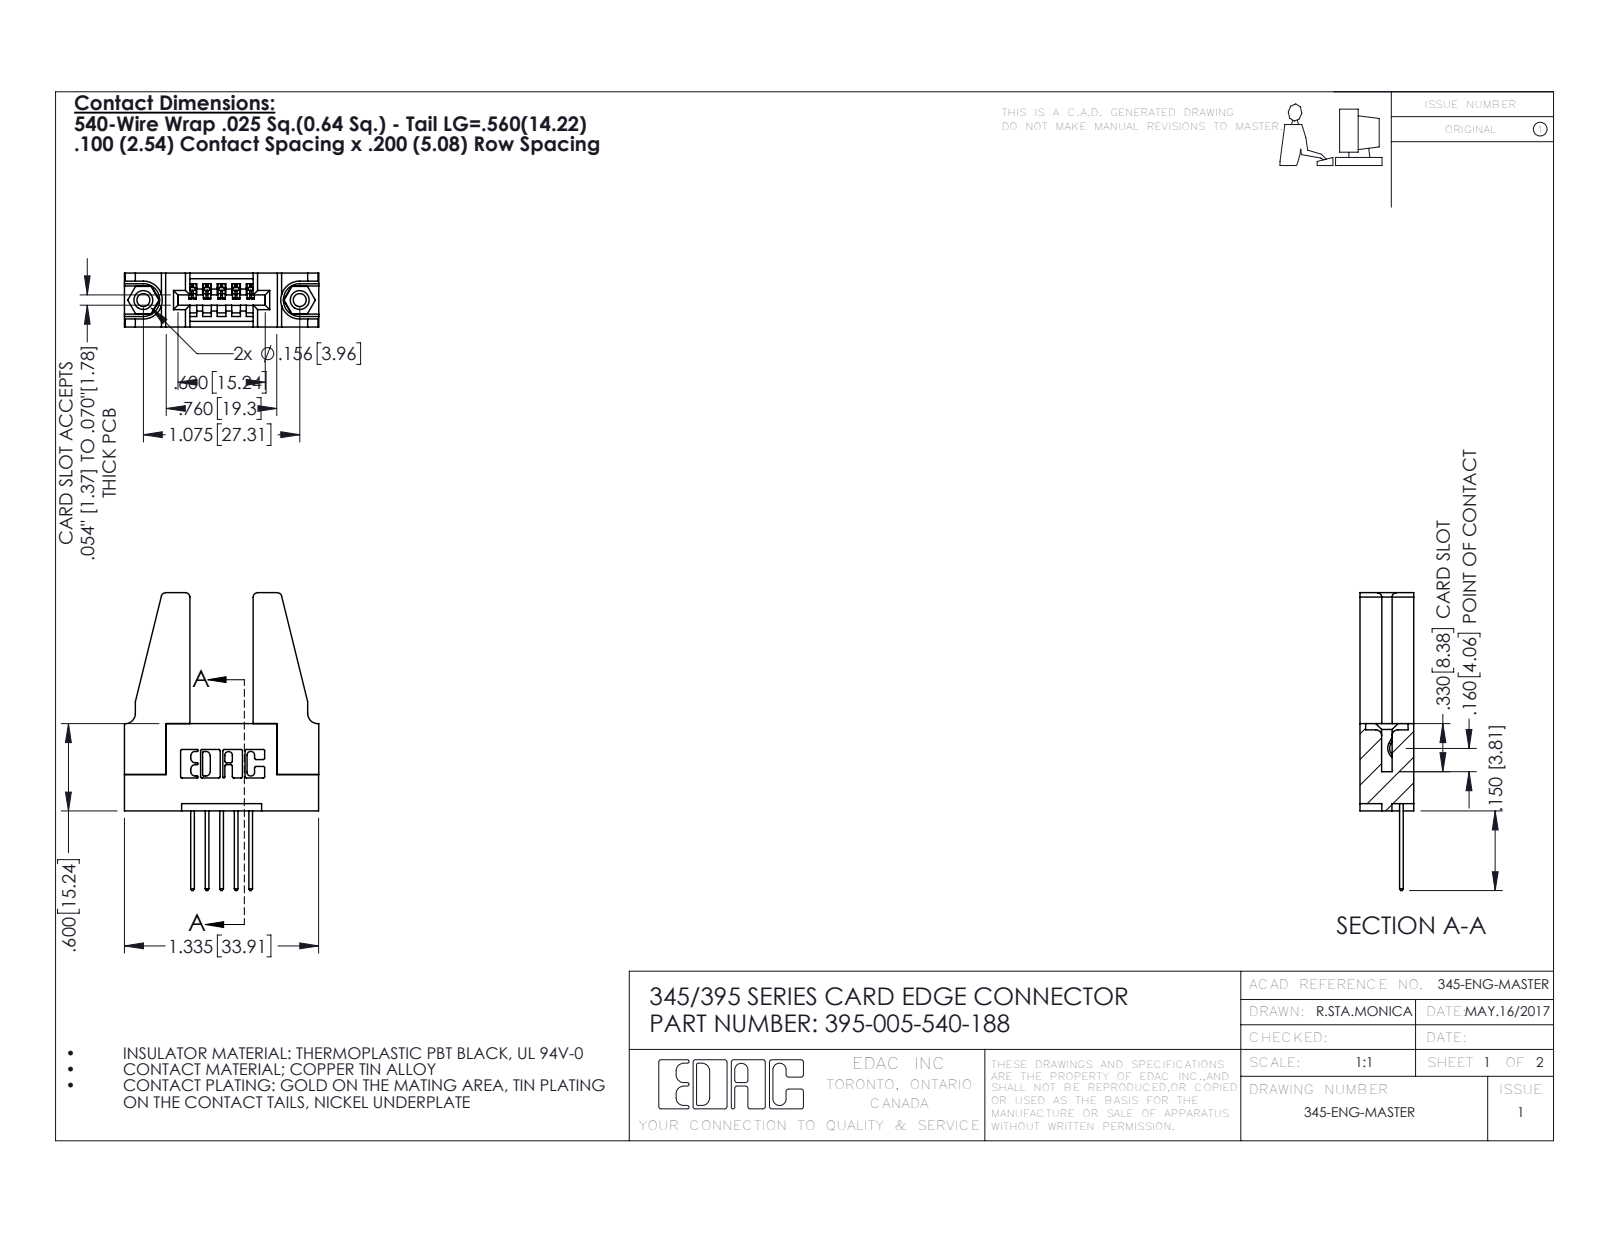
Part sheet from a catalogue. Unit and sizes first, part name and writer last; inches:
Units: inches
Overall size (bounding box): 2.047 × 1.336 × 0.37
Round holes (diameter × count): ⌀0.089 ×2, ⌀0.125 ×2, ⌀0.156 ×2, ⌀0.064 ×1
Round bosses / shafts (diameter × count): ⌀0.155 ×2
Partial cylindrical surfaces — rounded edges, fillets, slot ends (radius × count): R0.01 ×22, R0.006 ×10, R0.01 ×10, R0.03 ×8, R0.007 ×6, R0.031 ×6, R0.026 ×3, R0.031 ×2
Main face-to-face distances: 0.37, 0.2, 0.072, 0.298, 0.598, 0.25, 0.148, 0.15, 0.35, 0.077
Hole centre spacings: 0.27, 0.847, 1.075
Volume: 0.377 in³ · Surface area: 10.18 in²
Bodies: 10 solids, 540 faces (352 planar, 172 cylindrical, 16 other)
Part name (STEP PRODUCT): 345-292-001_345-293-140; 395-005-540-188; 345-250-001_345-250-001-102; 345 Part_Flush Mounting Lugs - 0.156 Dia-TH (+1 more)
STEP written by: SolidWorks 2016 (CONFIG_CONTROL_DESIGN)
